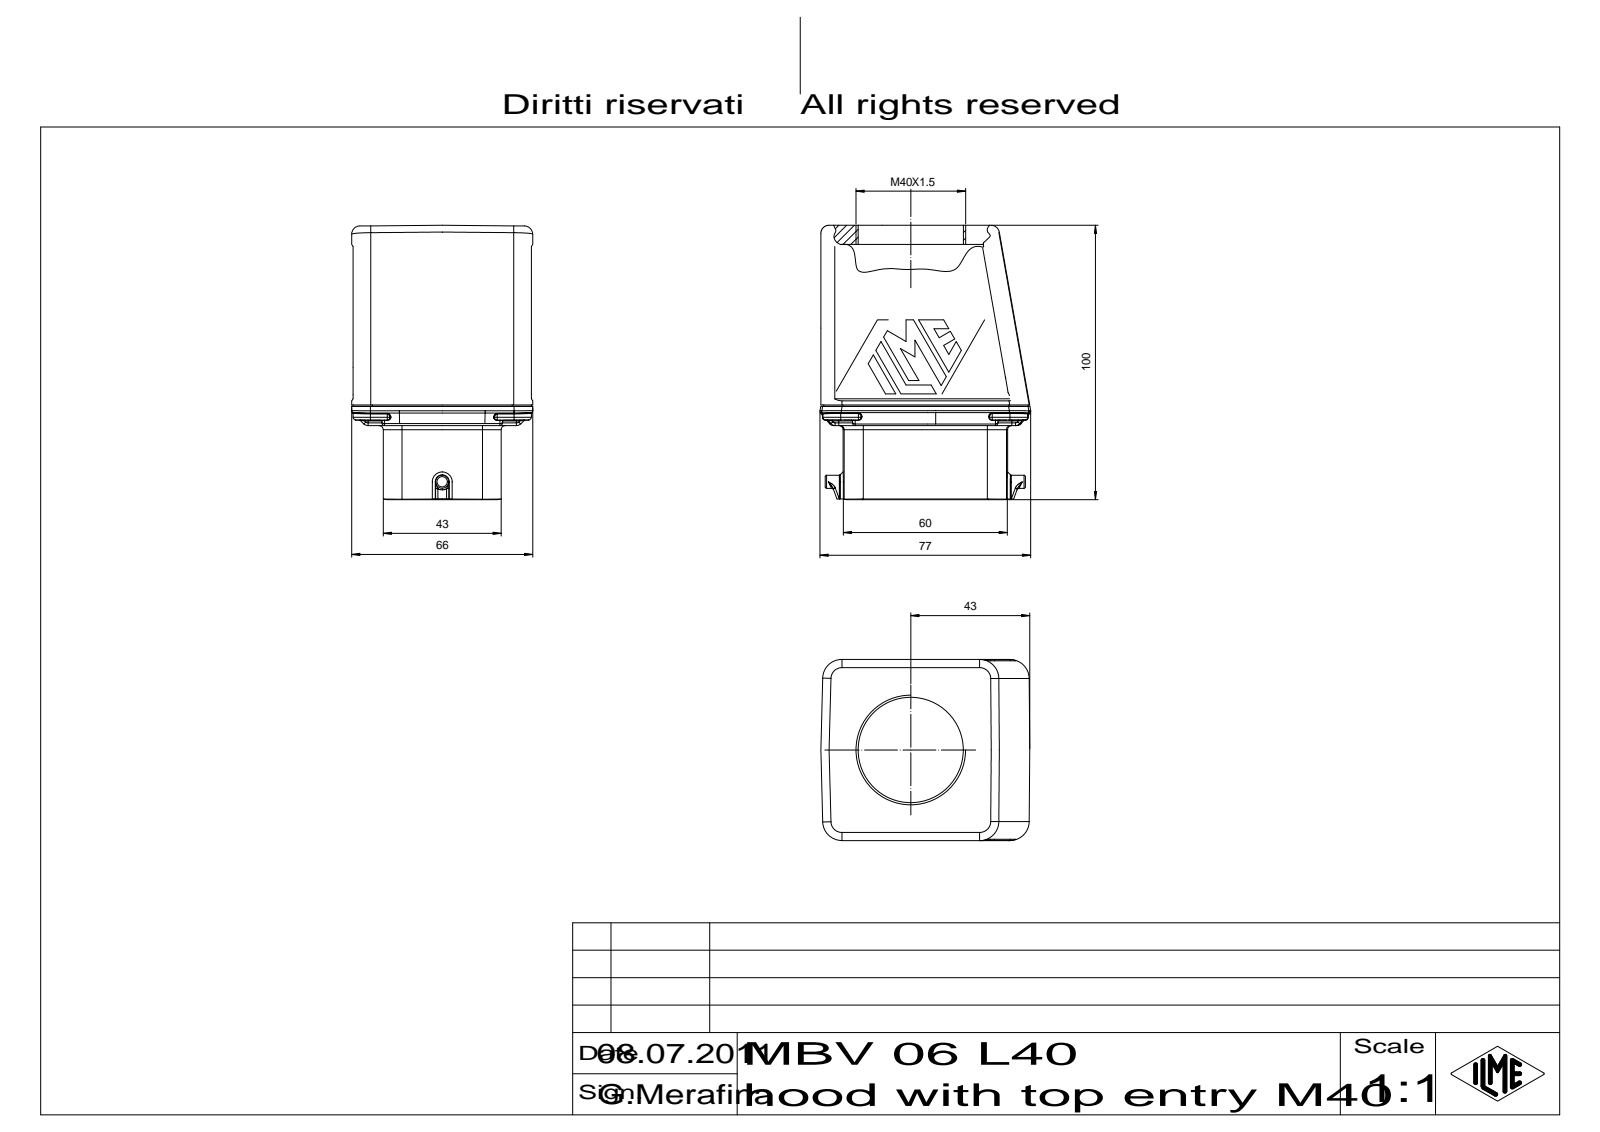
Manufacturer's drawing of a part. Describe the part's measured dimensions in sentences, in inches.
The part is named "53848_Body_1_Body_1.1". Its 3-D file was written by "CoCreate Modeling 16.00A 16-Aug-2008 (C) Parametric Technology GmbH (AUTOMOTIVE_DESIGN)". It is 1 solid with 561 faces: 265 planar, 140 cylindrical and 156 other. Overall it measures 3.917 by 2.983 by 2.599 inches. Its volume is 19.7 cubic inches and its surface area 63.32 square inches. Round holes: 1 of diameter 1.575. Round bosses or shafts: 1 of diameter 0.189. Partial cylindrical surfaces (rounded edges, fillets, slot ends): 46 of radius 0.039, 18 of radius 0.012, 14 of radius 0.276, 10 of radius 0.118, 6 of radius 0.059, 4 of radius 0.02, 4 of radius 0.165, 4 of radius 0.197. The main face-to-face distances are 2.863, 2.559, 0.016, 2.575, 0.709, 2.155, 0.433, 2.126, 2.126, 1.693.
